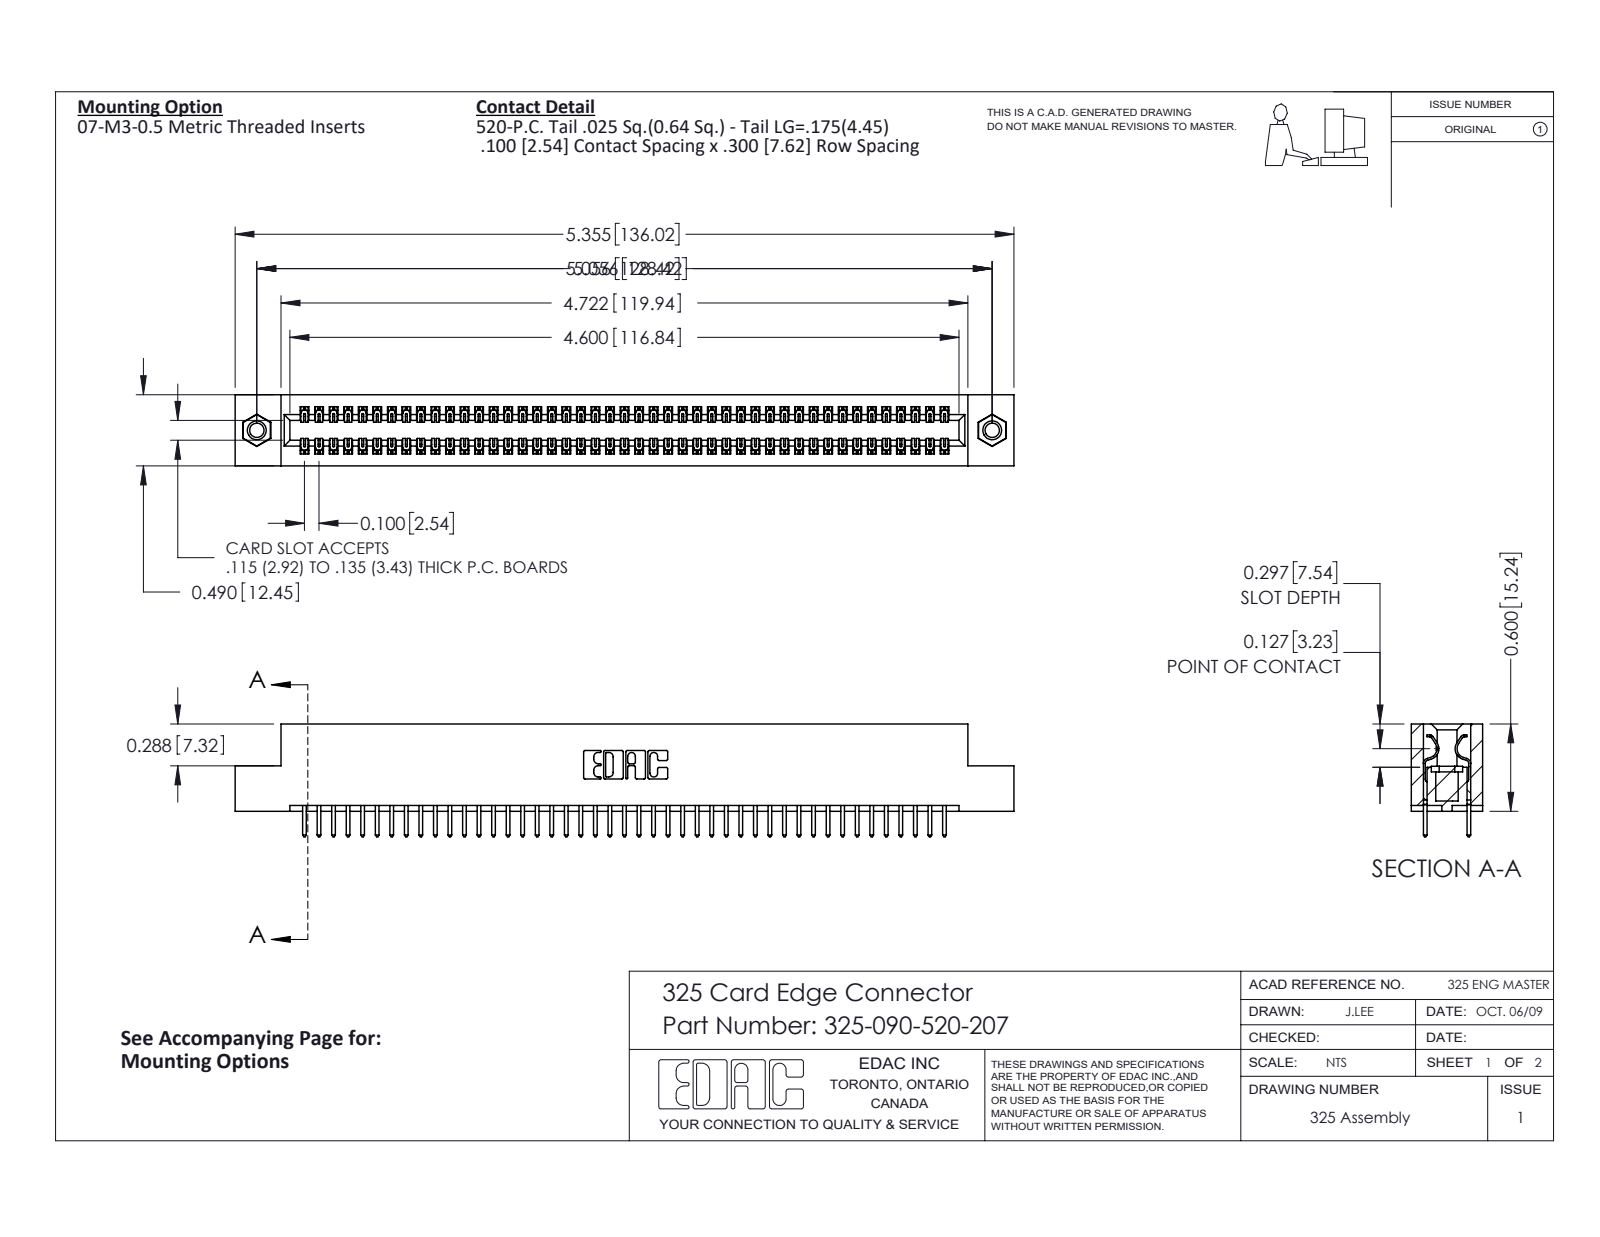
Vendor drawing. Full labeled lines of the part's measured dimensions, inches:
Part name (STEP PRODUCT): 325-292-001_325-293-120; 325 Part_TI; 325-090-520-207; 345-250-001_345-250-005-103
STEP written by: SolidWorks 2016 (CONFIG_CONTROL_DESIGN)
Units: inches
Bodies: 93 solids, 4854 faces (3342 planar, 1496 cylindrical, 16 other)
Overall size (bounding box): 5.355 × 0.775 × 0.49
Volume: 1.072 in³ · Surface area: 32.81 in²
Round holes (diameter × count): ⌀0.098 ×2, ⌀0.125 ×2, ⌀0.16 ×2
Round bosses / shafts (diameter × count): ⌀0.155 ×2
Partial cylindrical surfaces — rounded edges, fillets, slot ends (radius × count): R0.006 ×135, R0.01 ×90, R0.01 ×22, R0.007 ×6, R0.031 ×6, R0.026 ×3, R0.014 ×2, R0.022 ×2
Main face-to-face distances: 0.083, 0.407, 0.3, 0.49, 0.107, 0.383, 0.025, 0.325, 0.275, 0.56
Hole centre spacings: 5.056
